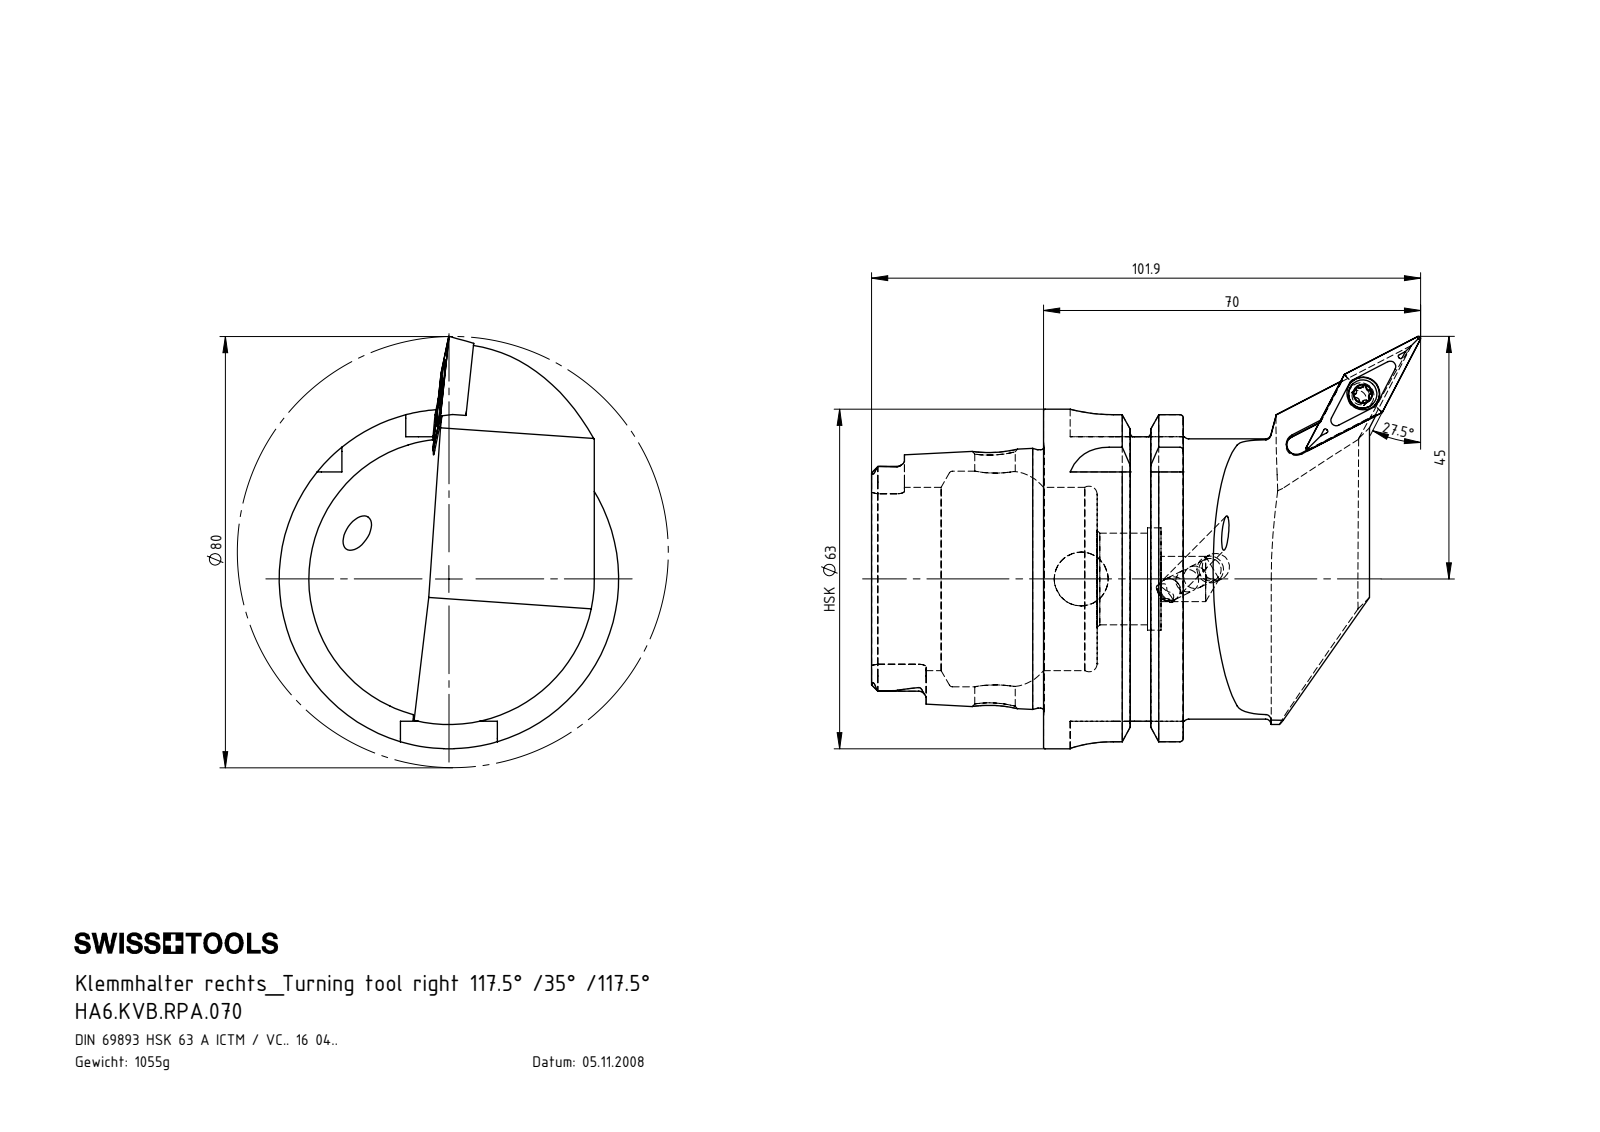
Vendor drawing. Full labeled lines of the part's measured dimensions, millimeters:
Part name (STEP PRODUCT): WCB-ER2.001.009_A; VCMT160404; HA6-KVB.RPA.070_C; KVT_MB_600_050 (+1 more)
STEP written by: SolidWorks 2017 (AUTOMOTIVE_DESIGN)
Units: millimetres
Bodies: 5 solids, 322 faces (84 planar, 89 cylindrical, 149 other)
Overall size (bounding box): 101.9 × 76.5 × 63
Volume: 129 435 mm³ · Surface area: 29 166 mm²
Round holes (diameter × count): ⌀4.2 ×2, ⌀3.3 ×1, ⌀4 ×1, ⌀4.4 ×1, ⌀5 ×1, ⌀6.1 ×1, ⌀7.5 ×1, ⌀8.4 ×1, ⌀10 ×1, ⌀17 ×1, ⌀19 ×1, ⌀34 ×1
Round bosses / shafts (diameter × count): ⌀63 ×1, ⌀54.95 ×1, ⌀52 ×1, ⌀47.94 ×1, ⌀5.25 ×1, ⌀5 ×1, ⌀4 ×1
Partial cylindrical surfaces — rounded edges, fillets, slot ends (radius × count): R0.34 ×6, R0.59 ×6, R1.4 ×6, R8 ×4, R2.82 ×2, R2.88 ×2, R1.75 ×1, R6 ×1
Main face-to-face distances: 25.95, 16, 9.95, 31.9, 41.85, 57.85, 52.8, 21.8, 11.85, 4.43
